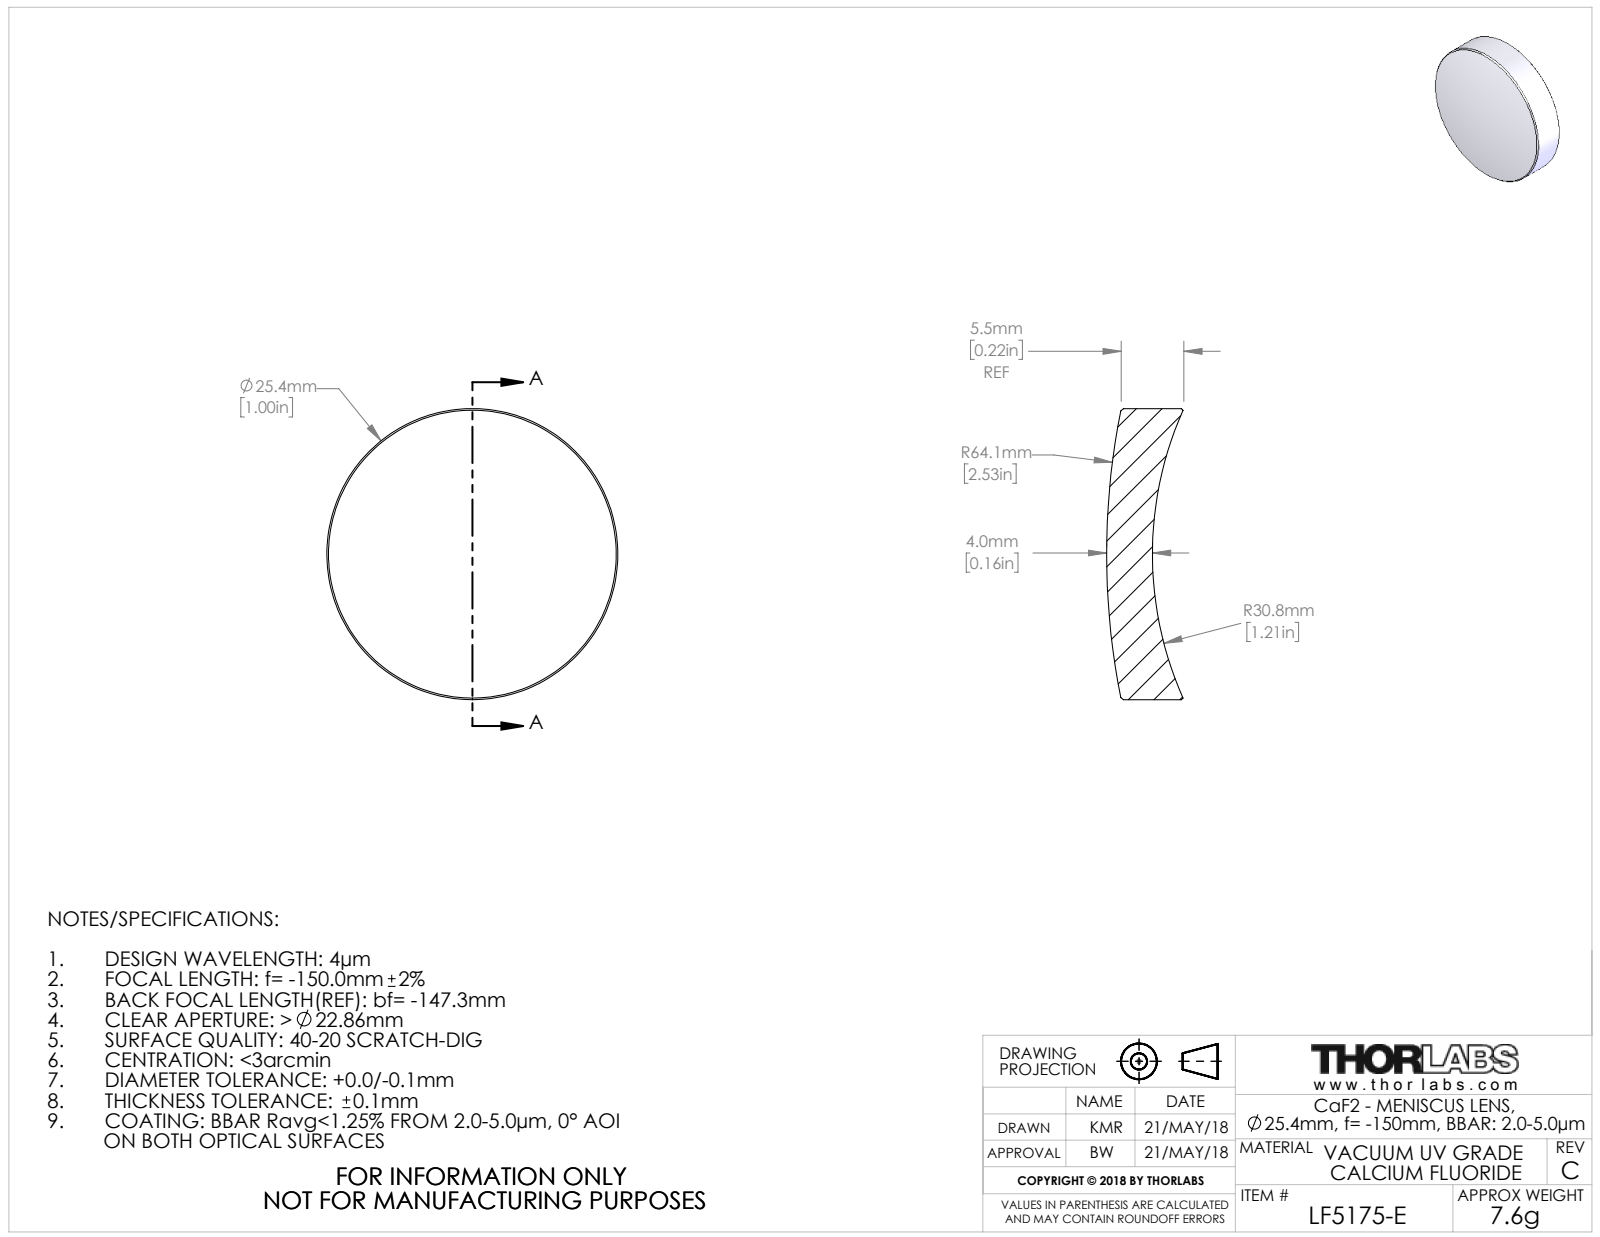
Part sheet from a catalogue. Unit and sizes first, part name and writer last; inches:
Units: inches
Overall size (bounding box): 1 × 1 × 0.263
Round bosses / shafts (diameter × count): ⌀1 ×1
Volume: 0.146 in³ · Surface area: 2.26 in²
Bodies: 1 solid, 10 faces (0 planar, 2 cylindrical, 8 other)
Part name (STEP PRODUCT): 20176-E0W
STEP written by: SolidWorks 2016 (CONFIG_CONTROL_DESIGN)
